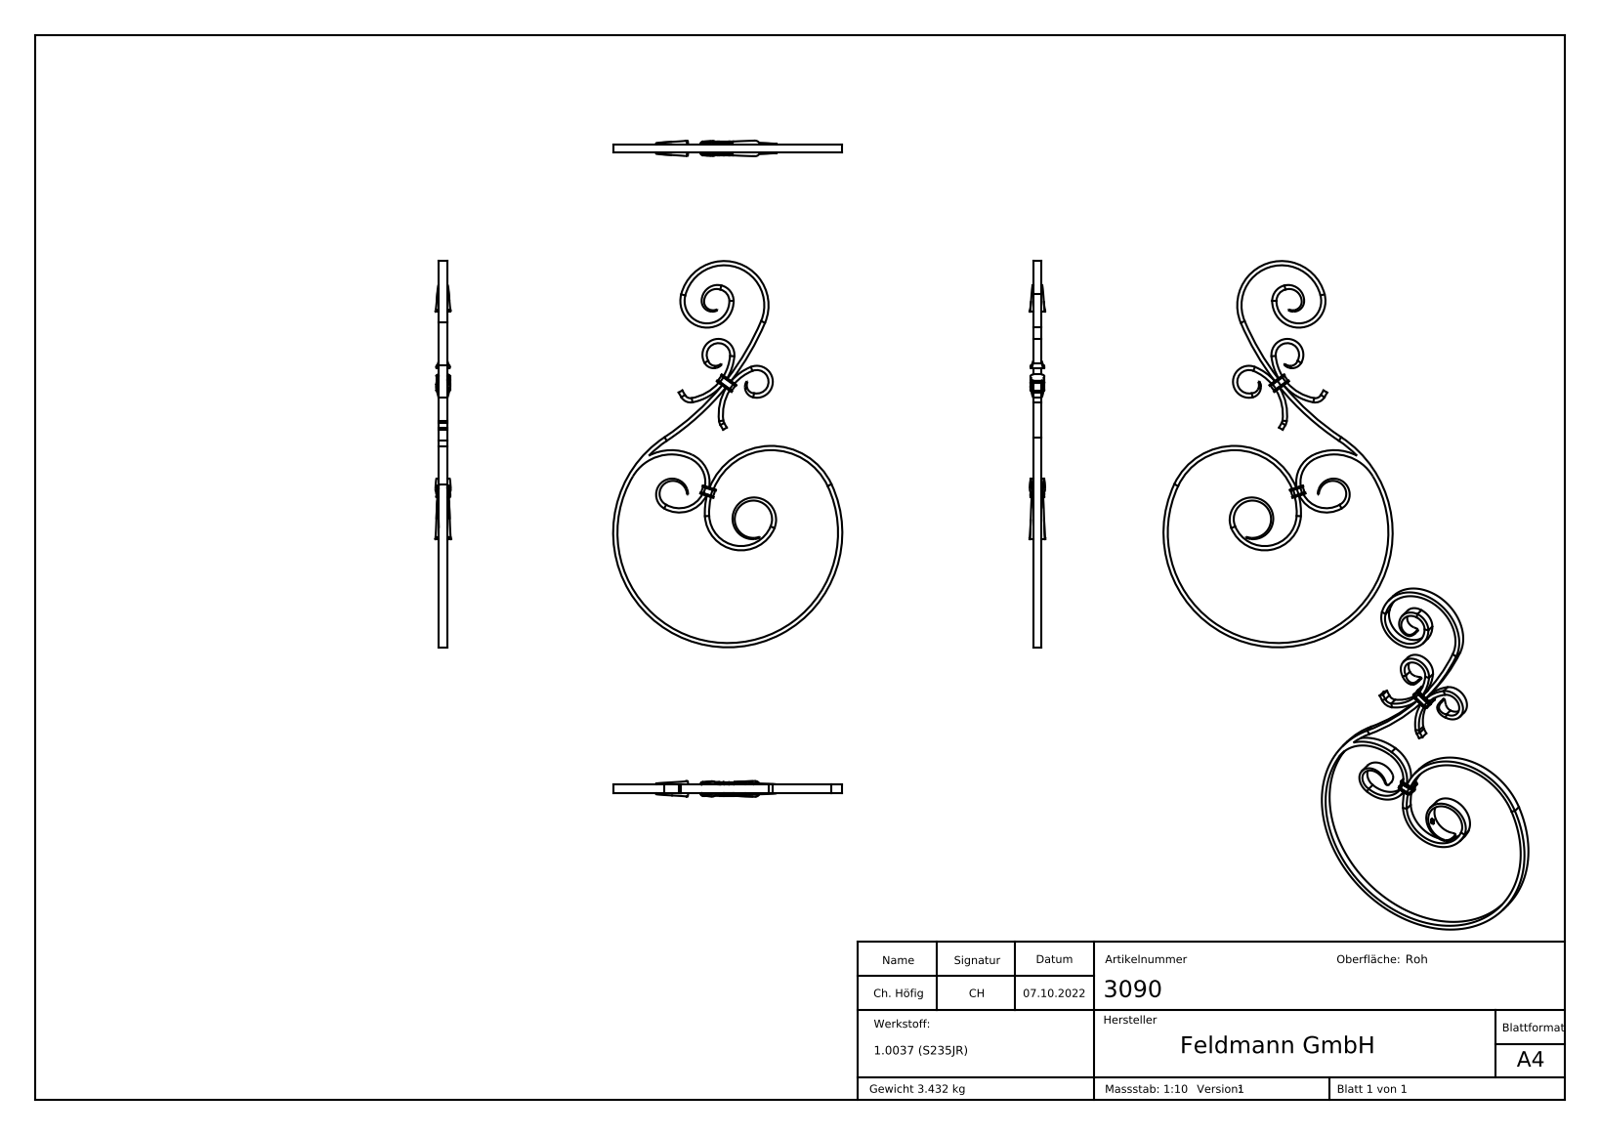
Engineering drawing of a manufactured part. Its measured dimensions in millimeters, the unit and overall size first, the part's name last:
Units: millimetres
Overall size (bounding box): 725 × 430 × 29.29
Partial cylindrical surfaces — rounded edges, fillets, slot ends (radius × count): R0.5 ×70, R18.5 ×10, R6 ×8, R22 ×3, R30 ×3, R12 ×2, R20 ×2, R88.49 ×2
Main face-to-face distances: 16, 8, 37.37, 2, 14, 15.99, 13.99, 45.37, 29.37, 1.99
Volume: 439 930 mm³ · Surface area: 171 142 mm²
Bodies: 1 solid, 613 faces (232 planar, 139 cylindrical, 242 other)
Part name (STEP PRODUCT): 3090
STEP written by: SolidWorks 2018 (CONFIG_CONTROL_DESIGN)
